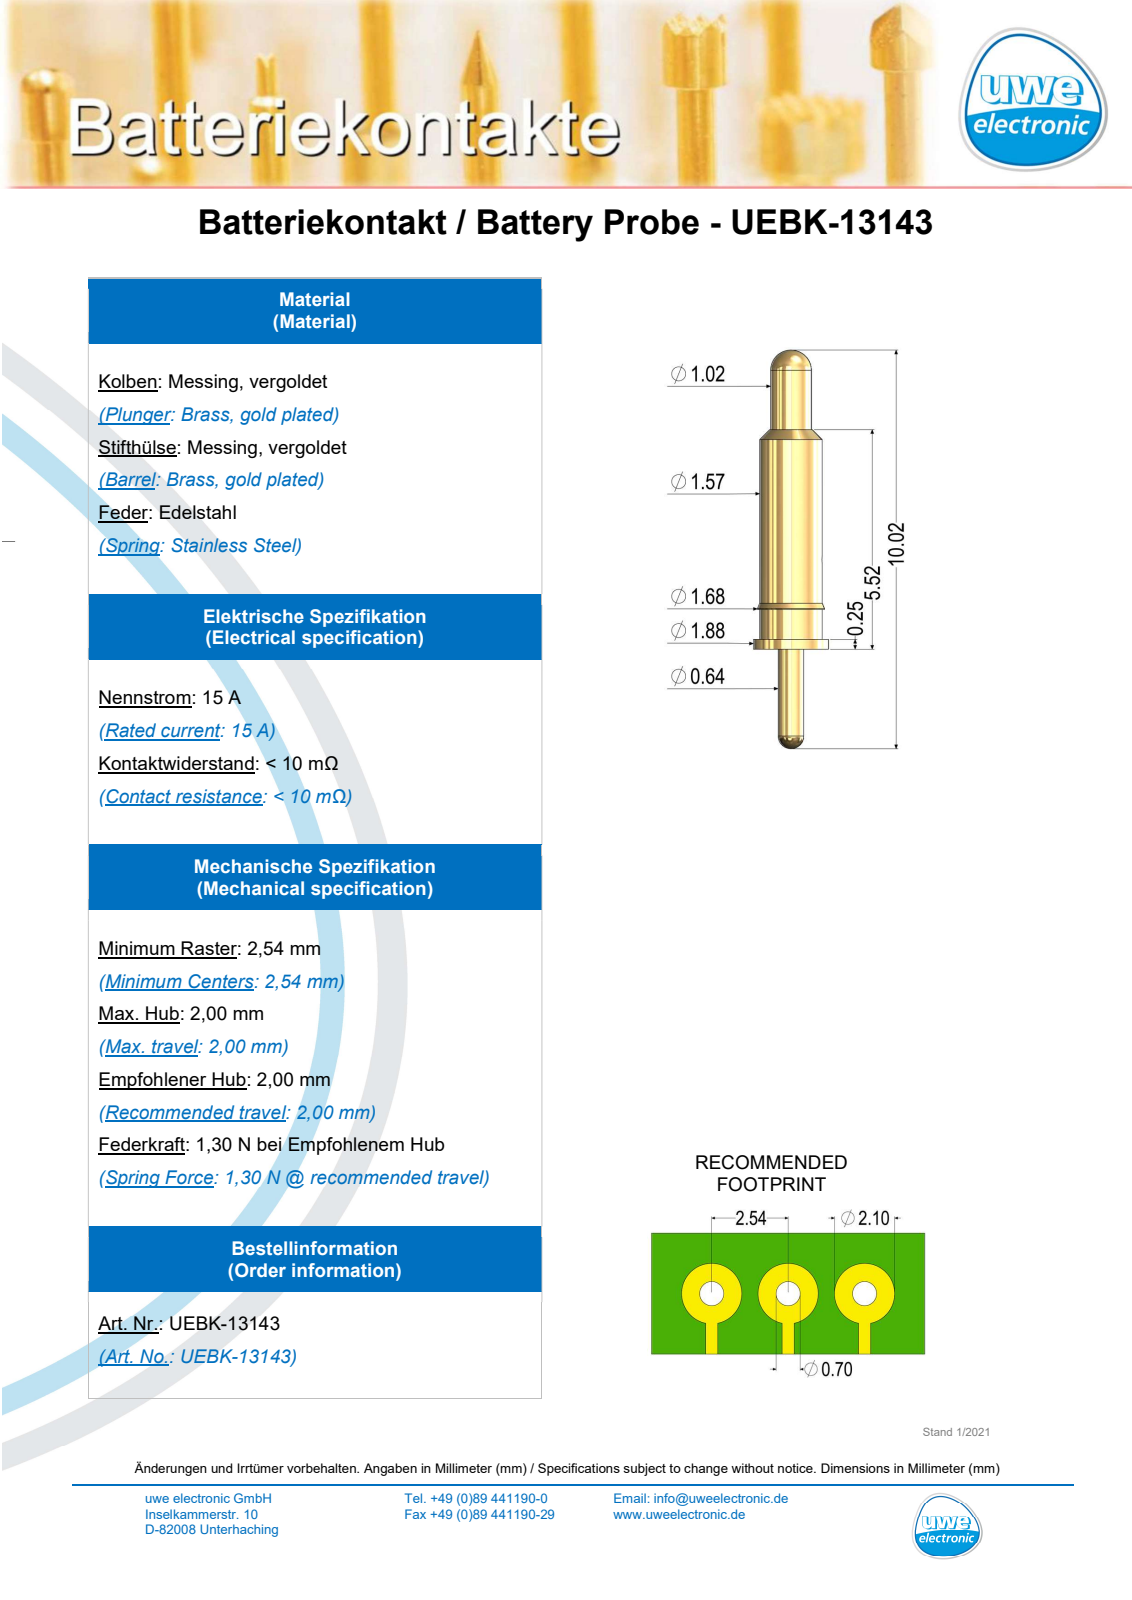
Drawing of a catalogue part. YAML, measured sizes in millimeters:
part_name: "UEBK-13143_2017_08_29"
step_written_by: "SolidWorks 2017 (AUTOMOTIVE_DESIGN)"
units: millimeters
bodies: {solids: 1, faces: 27, planar: 5, cylindrical: 14, other: 8}
overall_size: [10.02, 1.88, 1.88]
volume: 13
surface_area: 43
round_holes:
  - {diameter: 0.2, count: 1}
round_bosses_or_shafts:
  - {diameter: 1.88, count: 1}
  - {diameter: 1.68, count: 1}
  - {diameter: 1.57, count: 1}
  - {diameter: 1.02, count: 1}
  - {diameter: 0.64, count: 1}
face_to_face_distances: [0.75, 1, 4.52, 5.27, 5.52]
